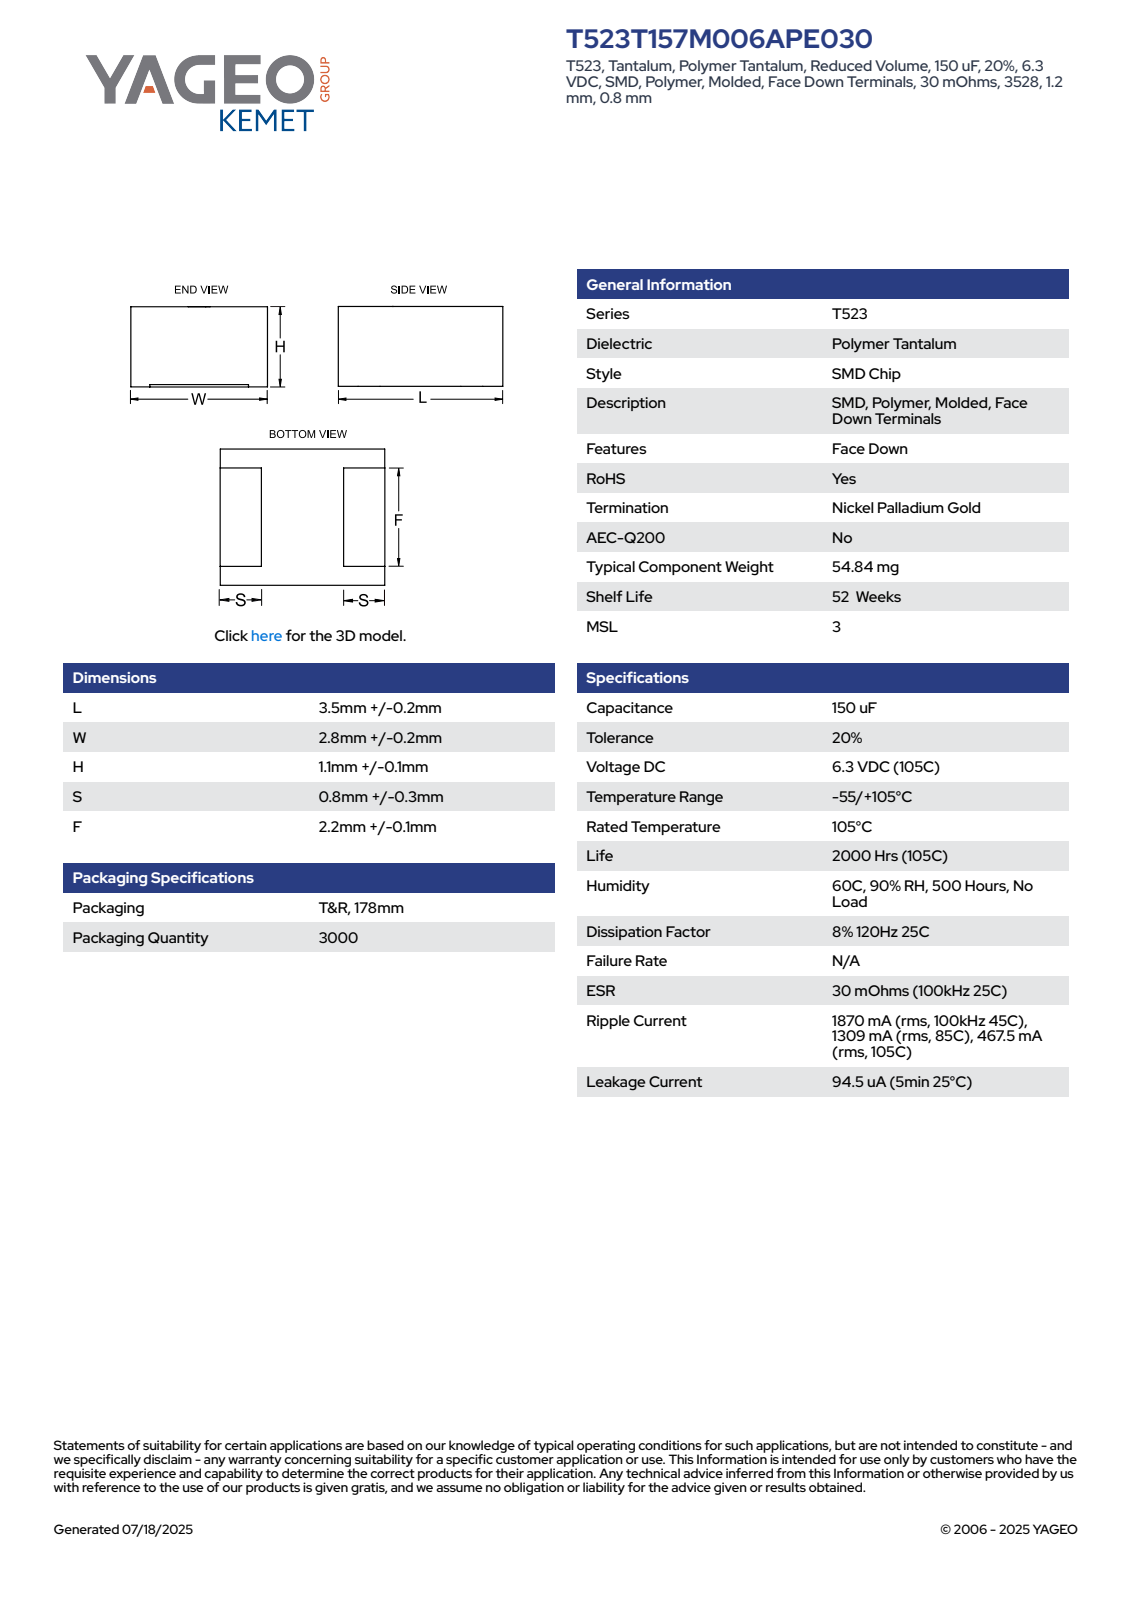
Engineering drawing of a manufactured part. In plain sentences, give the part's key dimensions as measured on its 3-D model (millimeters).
The part is named "CTS_TFD_3528_L3.7W3H1.2S0.8F2.3". Its 3-D file was written by "SolidWorks 2020 (AUTOMOTIVE_DESIGN)". It is 4 solids with 95 faces: 95 planar, 0 cylindrical and 0 other. Overall it measures 3.71 by 3 by 1.21 millimeters. Its volume is 13 cubic millimeters and its surface area 40 square millimeters. The main face-to-face distances are 1.2, 3, 3.7, 1.21, 3.71, 3.72, 0.8, 0.81, 2.91, 2.9.
